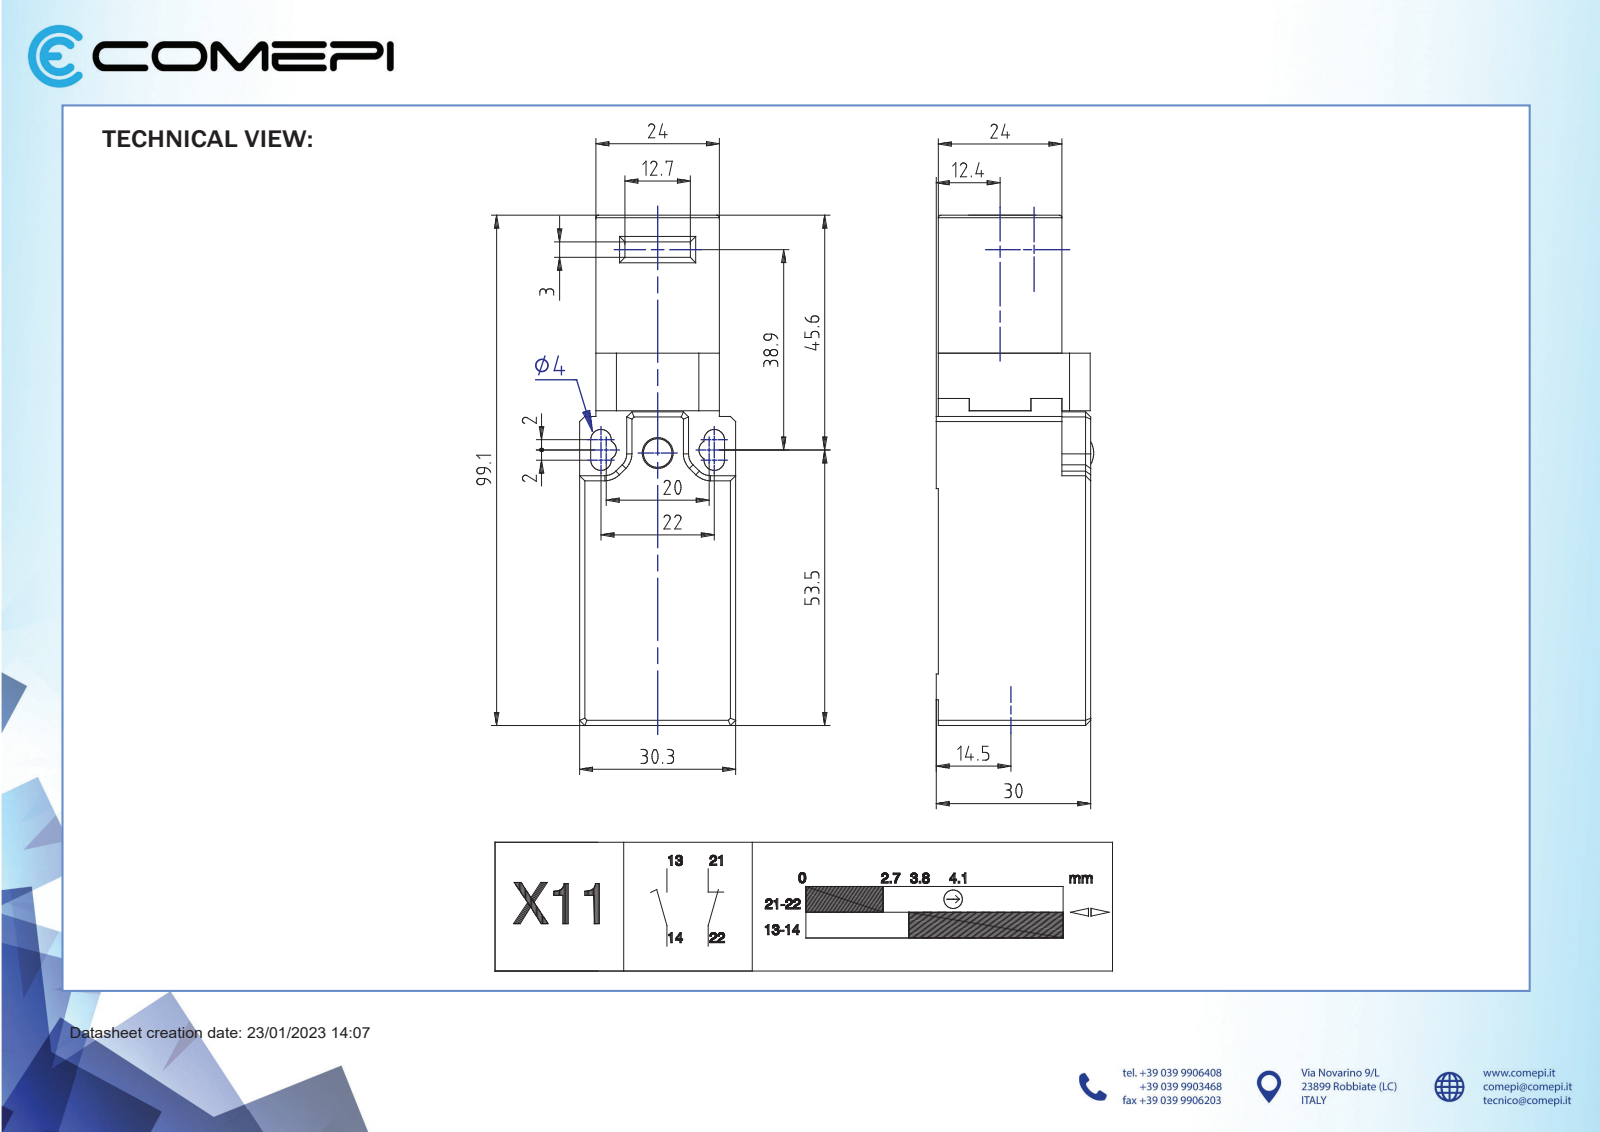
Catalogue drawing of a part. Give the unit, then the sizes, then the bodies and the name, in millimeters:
Units: millimetres
Overall size (bounding box): 99.6 × 36.6 × 30.3
Round holes (diameter × count): ⌀6 ×1, ⌀15 ×1, ⌀17 ×1, ⌀19 ×1
Round bosses / shafts (diameter × count): ⌀5.6 ×1
Partial cylindrical surfaces — rounded edges, fillets, slot ends (radius × count): R2 ×30, R0.4 ×24, R0.5 ×4, R3 ×4, R1.5 ×2, R2.3 ×2, R10 ×1, R10.2 ×1
Main face-to-face distances: 3.1, 27.2, 24, 30.3, 30, 29.6, 6, 0.4, 30.4, 2
Hole centre spacings: 2.1
Volume: 76 230 mm³ · Surface area: 23 370 mm²
Bodies: 4 solids, 262 faces (173 planar, 80 cylindrical, 9 other)
Part name (STEP PRODUCT): SP2K80X11
STEP written by: SolidWorks 2021 (AUTOMOTIVE_DESIGN)
